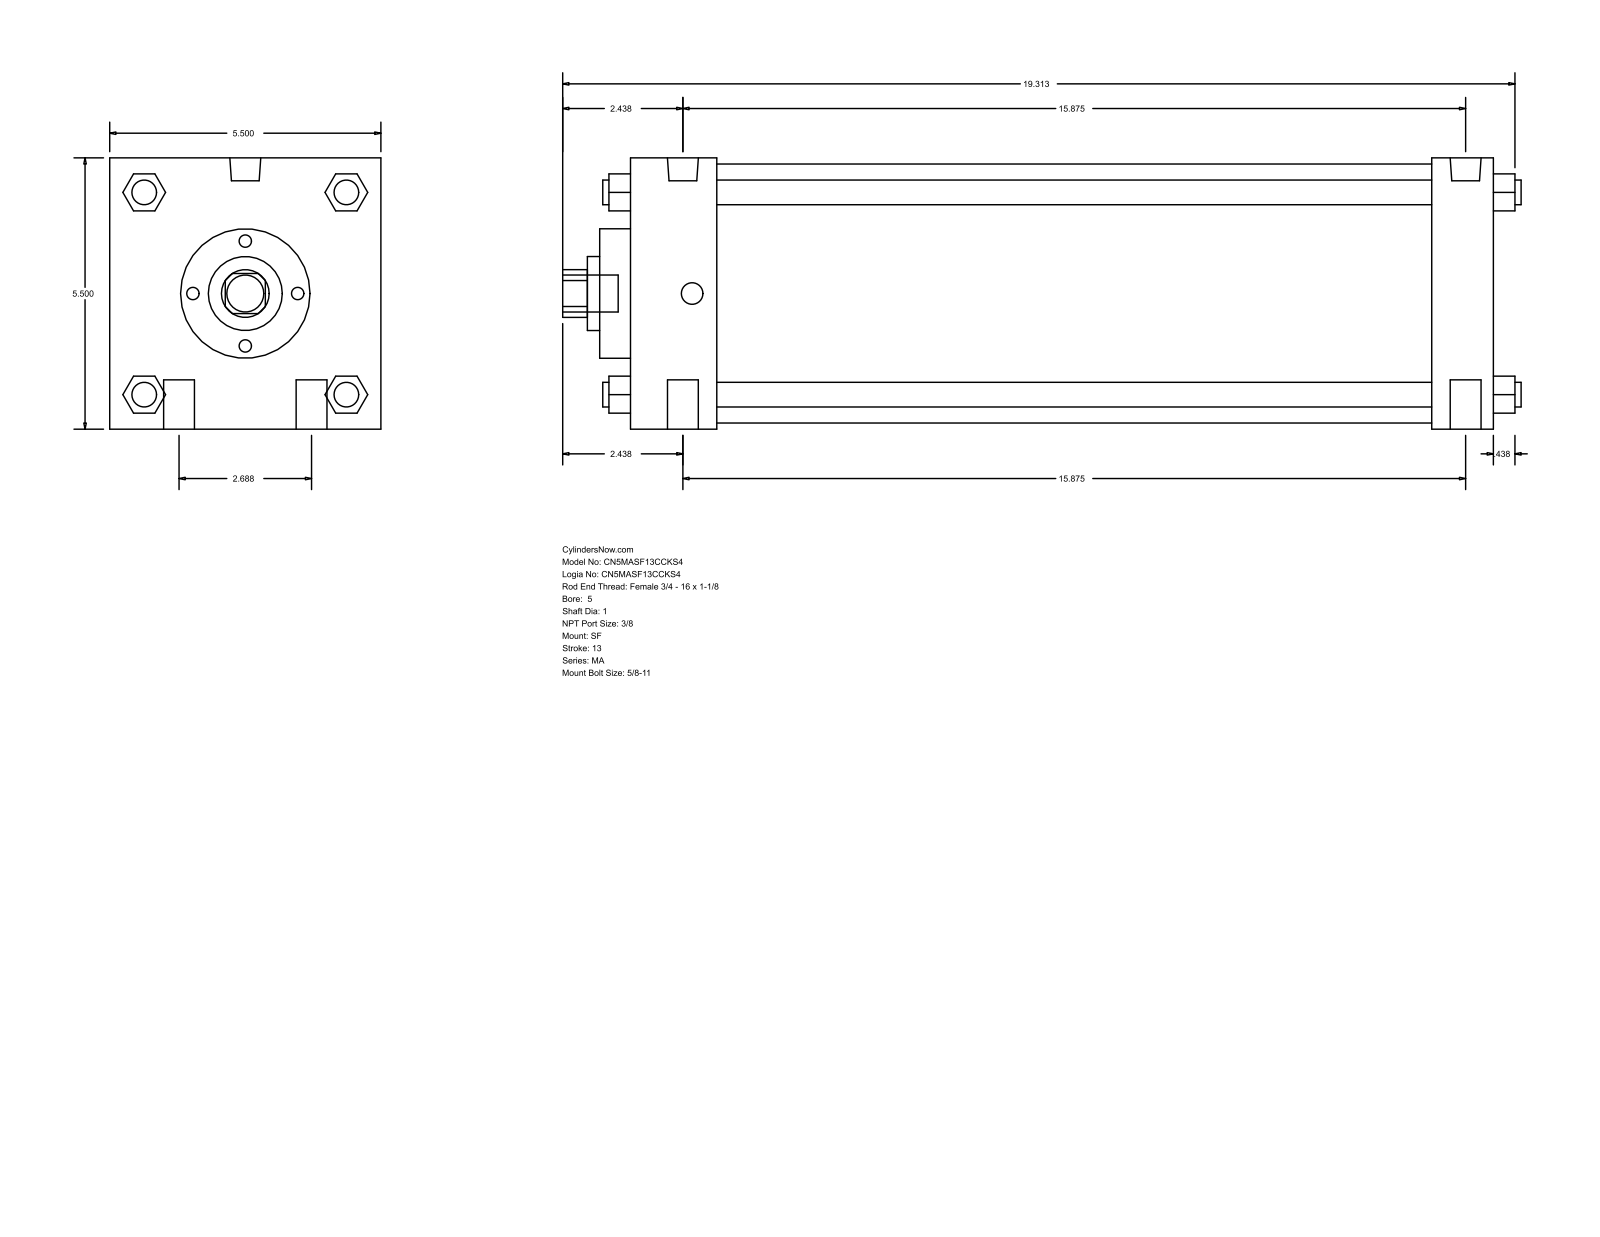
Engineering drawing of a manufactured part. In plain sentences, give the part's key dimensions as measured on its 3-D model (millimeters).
The part is named "MA_SF__0500_1". Its 3-D file was written by "GSSL Pune (CONFIG_CONTROL_DESIGN)". It is 0 solids with 126 faces: 95 planar, 31 cylindrical and 0 other. Overall it measures 493.71 by 139.7 by 139.7 millimeters. Round holes: 1 of diameter 25.4, 1 of diameter 38.1, 1 of diameter 66.67, 1 of diameter 133.35. Round bosses or shafts: 4 of diameter 15.88, 4 of diameter 12.7, 2 of diameter 15.93, 2 of diameter 11.11, 1 of diameter 19.05. Partial cylindrical surfaces (rounded edges, fillets, slot ends): 1 of radius 12.29. The main face-to-face distances are 139.7, 444.51, 44.46, 412.76, 368.3, 400.05, 31.75, 15.87, 60.33, 428.63.
